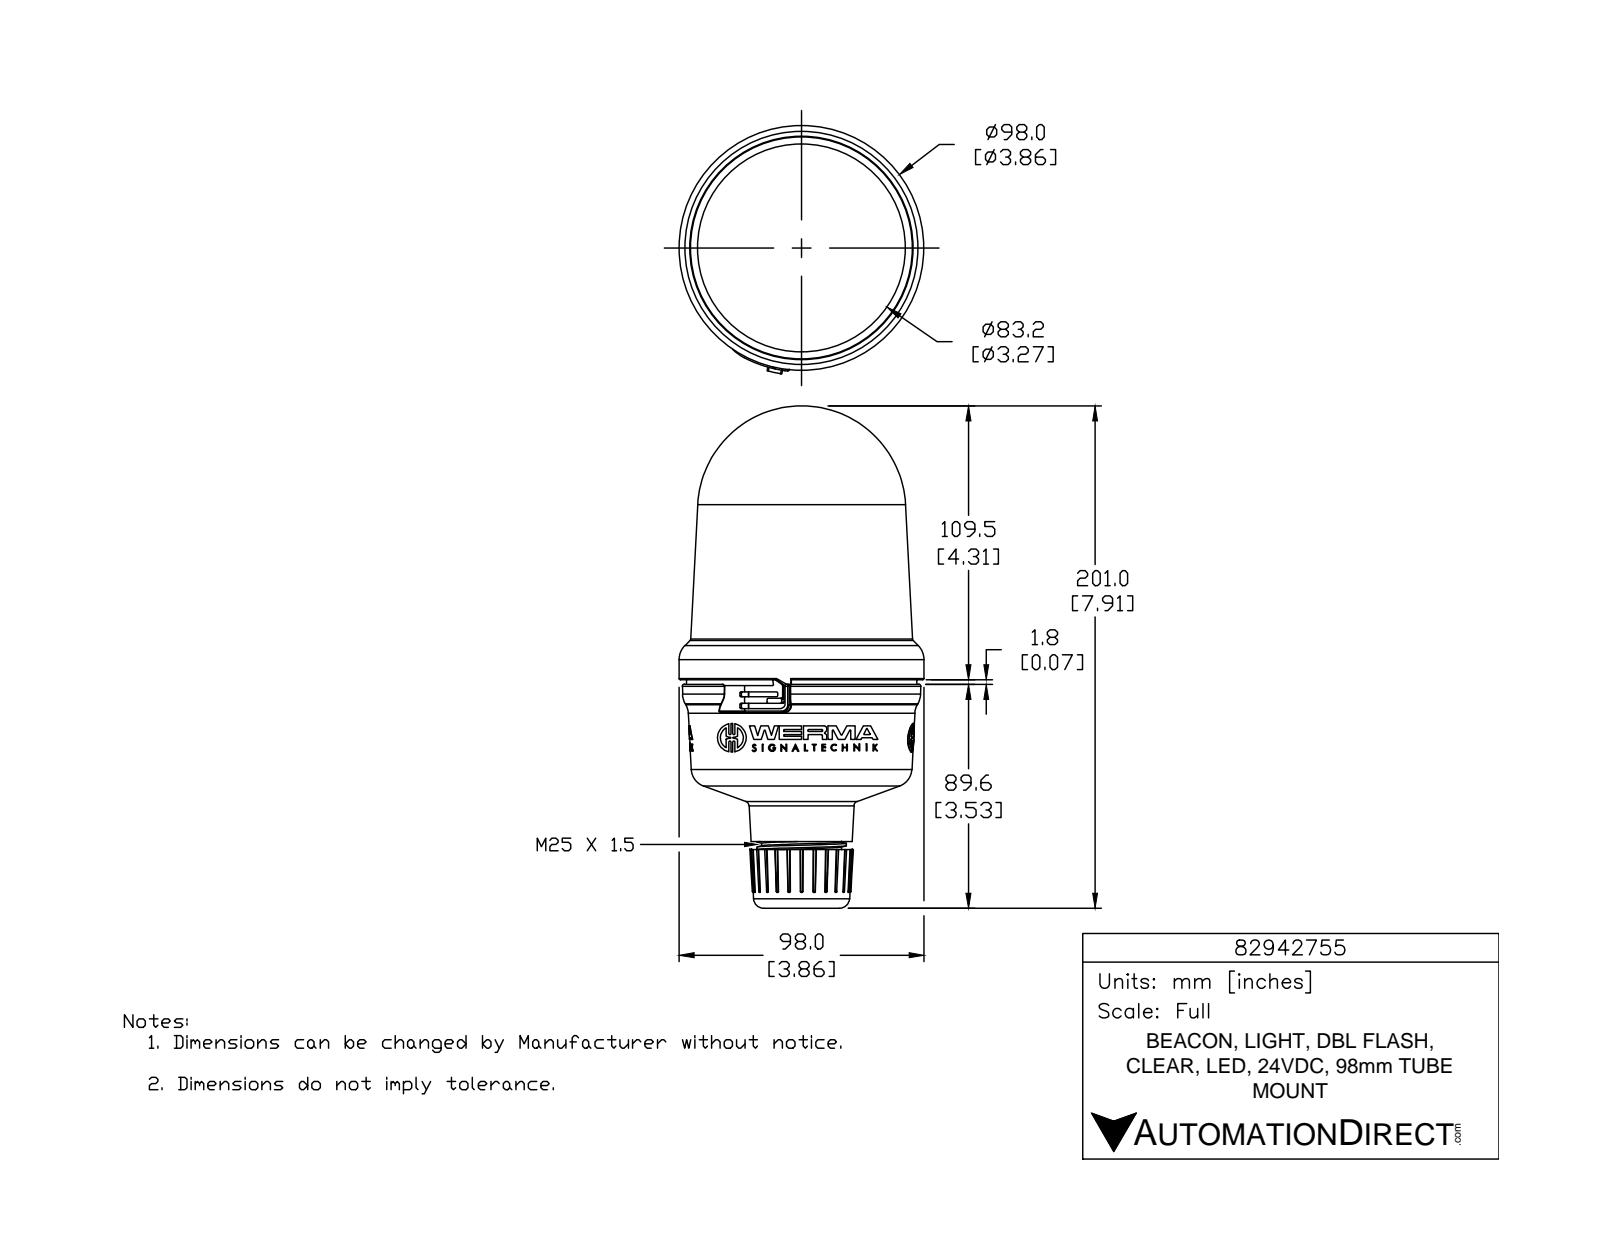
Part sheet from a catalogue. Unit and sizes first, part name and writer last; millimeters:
Units: millimetres
Overall size (bounding box): 201 × 99.4 × 98
Round holes (diameter × count): ⌀2 ×3, ⌀25.7 ×1, ⌀26 ×1
Round bosses / shafts (diameter × count): ⌀11.5 ×3, ⌀2.9 ×3, ⌀98 ×1, ⌀35.8 ×1, ⌀32 ×1
Partial cylindrical surfaces — rounded edges, fillets, slot ends (radius × count): R0.5 ×12, R0.2 ×9, R0.2 ×6, R0.4 ×6, R0.4 ×6, R0.4 ×6, R6.7 ×6, R0.2 ×3
Main face-to-face distances: 56.2, 11.7, 68, 8.5, 3.2, 64.7, 66.1, 62.9, 54.4, 1.9
Volume: 896 400 mm³ · Surface area: 58 960 mm²
Bodies: 1 solid, 1006 faces (554 planar, 189 cylindrical, 263 other)
Part name (STEP PRODUCT): 82942755
STEP written by: SolidWorks 2015 (AUTOMOTIVE_DESIGN)
